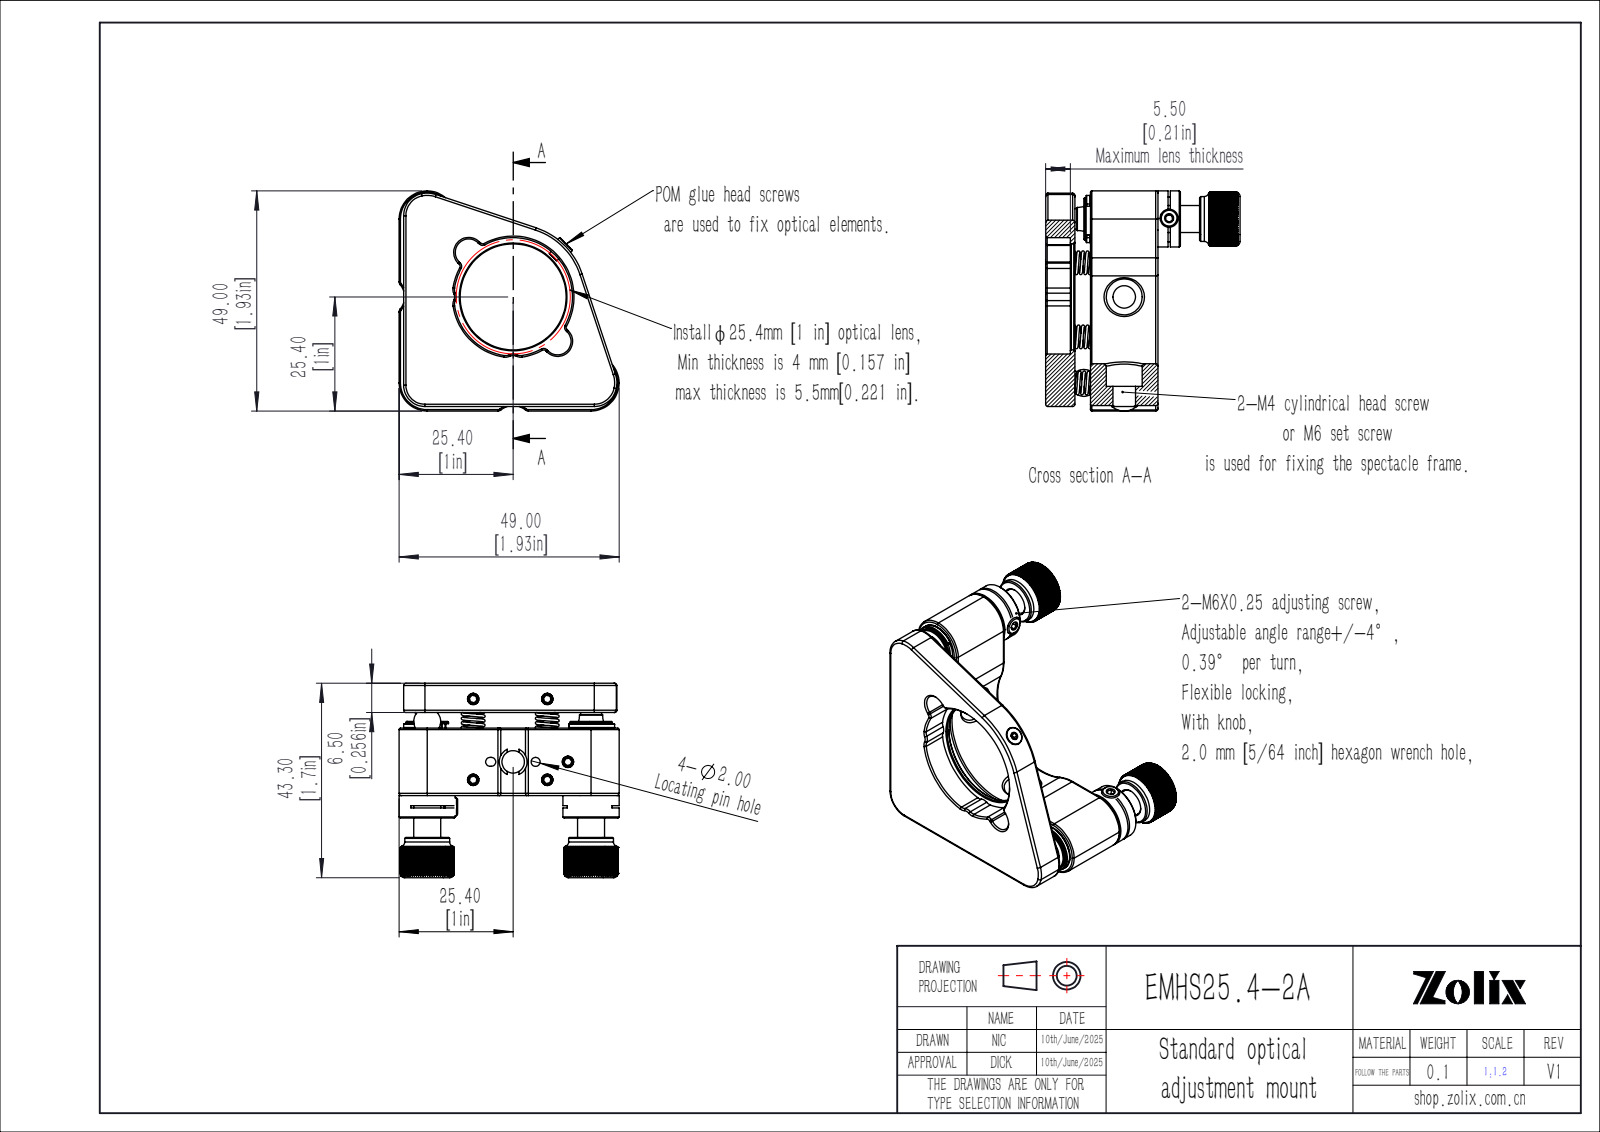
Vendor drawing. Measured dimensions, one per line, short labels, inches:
name: EMHS25.4-2A
written by: SolidWorks 2020 (CONFIG_CONTROL_DESIGN)
unit: in
bodies: 0 solids, 1056 faces (471 planar, 322 cylindrical, 263 other)
size: 1.929 × 1.929 × 1.705
holes: 4× ⌀0.118, 4× ⌀0.236, 2× ⌀0.394, 2× ⌀0.492, 1× ⌀0.13, 1× ⌀0.181, 1× ⌀0.248, 1× ⌀0.929
bosses: 5× ⌀0.157, 4× ⌀0.118, 3× ⌀0.315, 2× ⌀0.374, 2× ⌀0.236, 2× ⌀0.197, 2× ⌀0.079, 2× ⌀0.059
rounds: 12× R0.02, 12× R0.039, 6× R0.079, 5× R0.012, 4× R0.031, 3× R0.246, 2× R0.118, 2× R0.122
face distances: 0.256, 0.728, 0.984, 0.138, 0.394, 0.591, 0.039, 0.089, 0.108, 0.453
hole spacings: 0.65, 0.384, 0.811, 0.831, 1.017, 1.033, 1.128, 1.493
